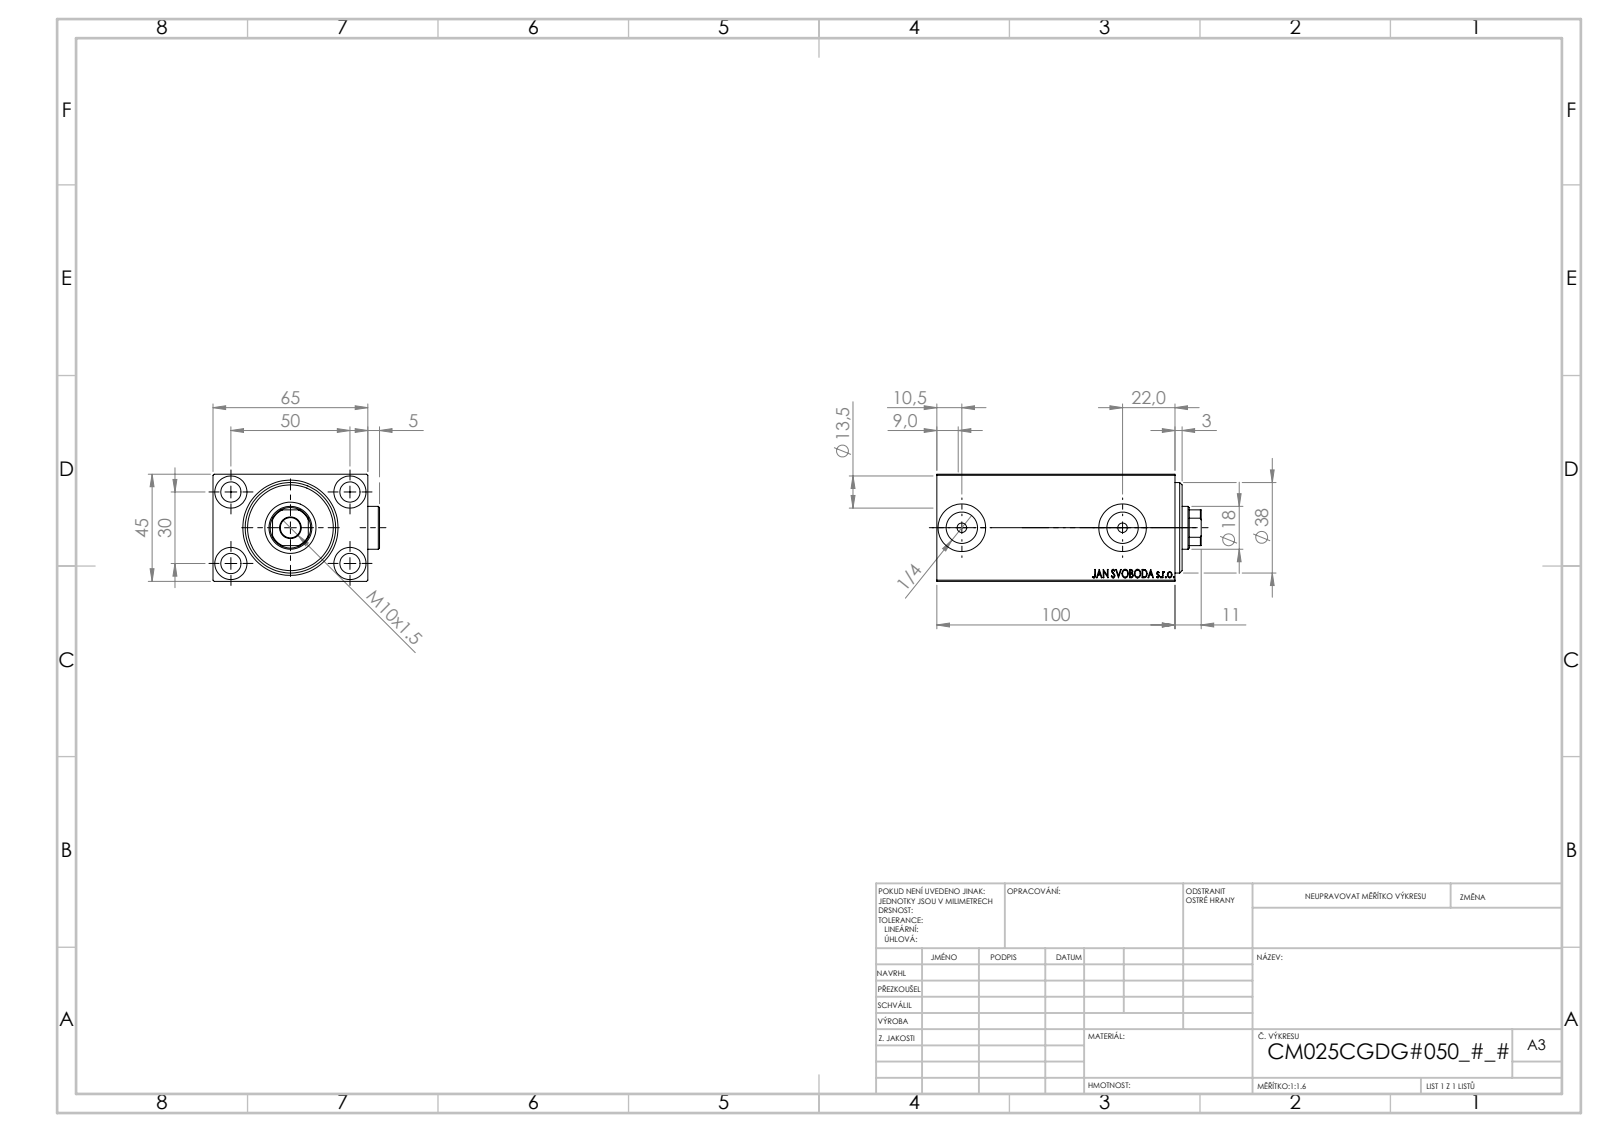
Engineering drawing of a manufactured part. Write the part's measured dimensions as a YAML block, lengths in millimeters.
part_name: "V450CM_VC_B; Zatka_OIL_PORT; V450CM_C_VCP; V450CM_C_Body"
step_written_by: "SolidWorks 2019 (CONFIG_CONTROL_DESIGN)"
units: millimeters
bodies: {solids: 4, faces: 916, planar: 442, cylindrical: 76, other: 398}
overall_size: [111, 69.9, 45]
volume: 44429
surface_area: 59411
round_holes:
  - {diameter: 8.5, count: 5}
  - {diameter: 13.5, count: 4}
  - {diameter: 4, count: 2}
  - {diameter: 13.16, count: 2}
  - {diameter: 20, count: 2}
  - {diameter: 18, count: 1}
  - {diameter: 21.5, count: 1}
  - {diameter: 25, count: 1}
  - {diameter: 27, count: 1}
  - {diameter: 38, count: 1}
round_bosses_or_shafts:
  - {diameter: 18, count: 2}
partial_cylinders:
  - {radius: 8.5, count: 1}
face_to_face_distances: [45, 65, 5, 6, 89, 94, 64.9, 100, 95, 3]
hole_center_spacings: [29.15, 30, 50, 58.31, 67.5]
